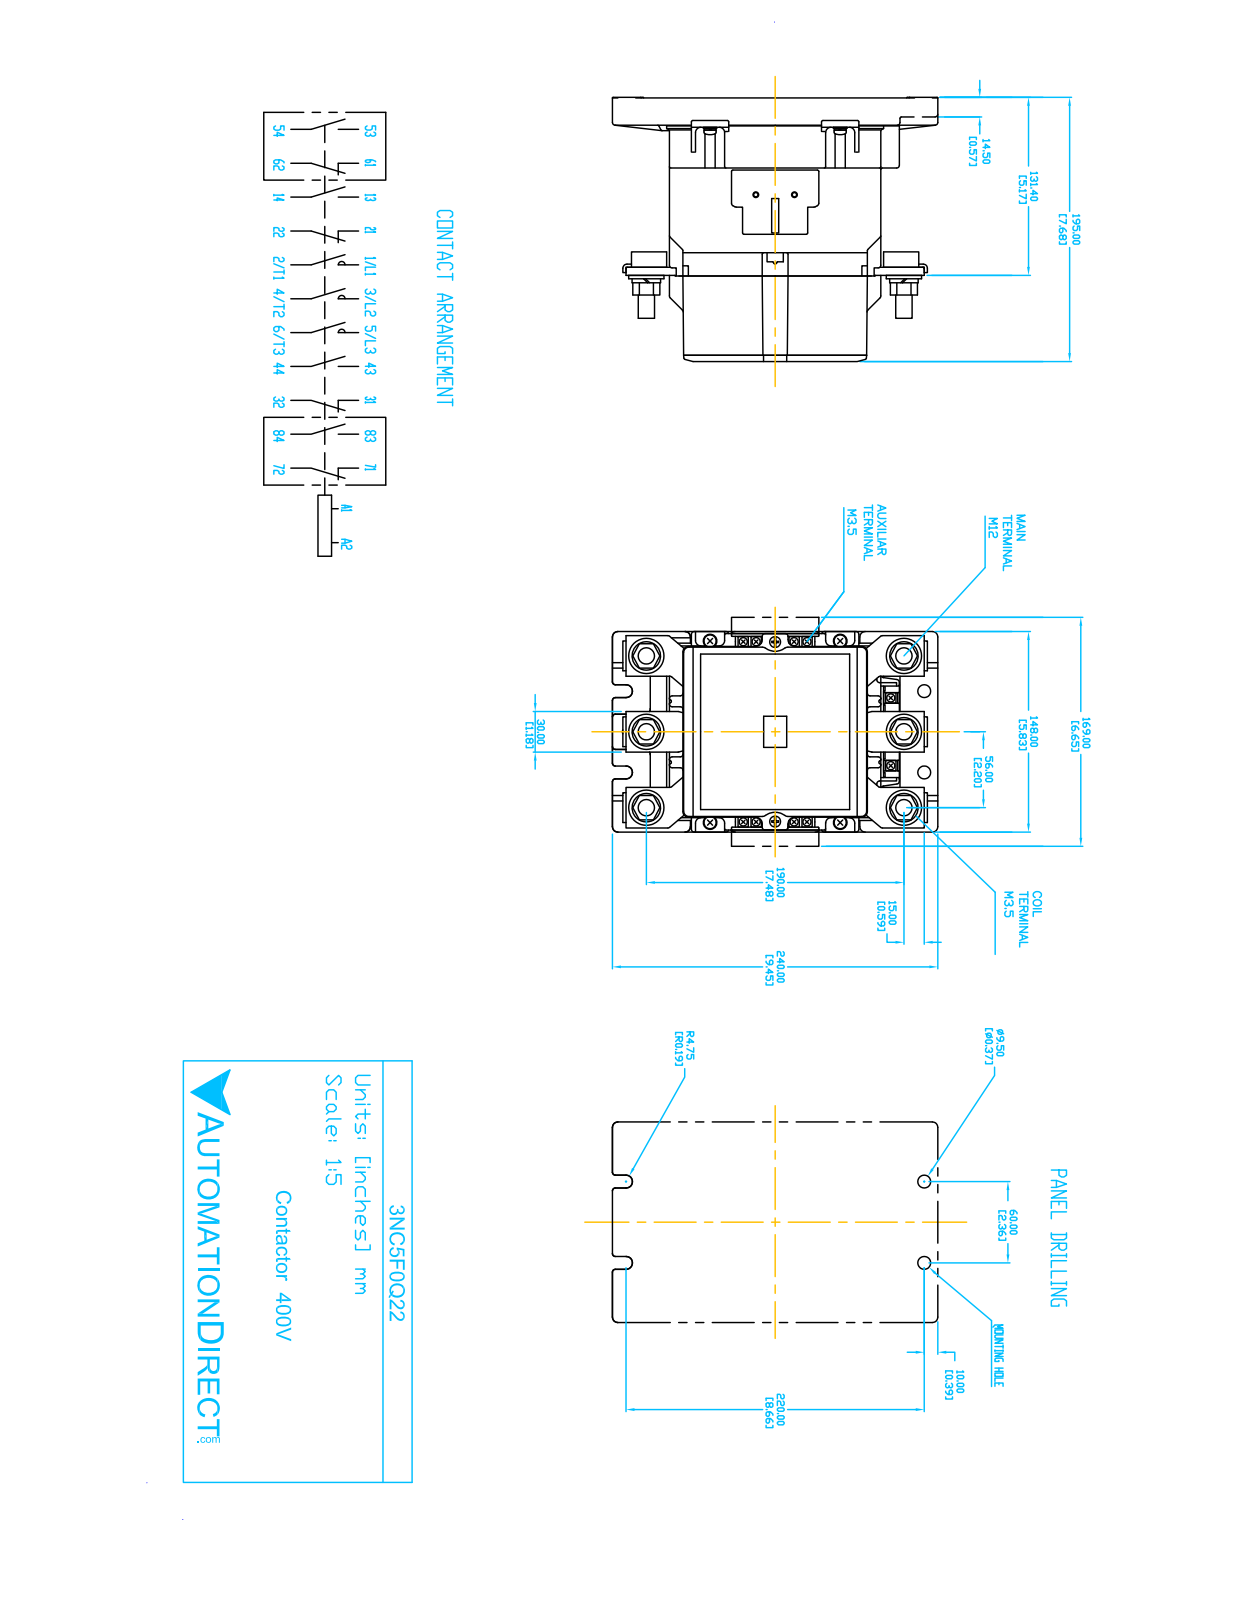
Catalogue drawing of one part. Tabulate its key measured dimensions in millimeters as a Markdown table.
| quantity | value |
| --- | --- |
| part name | 3NC5F0Q22 |
| STEP written by | SolidWorks 2018 (AUTOMOTIVE_DESIGN) |
| units | millimeters |
| bodies | 20 solids, 375 faces (261 planar, 114 cylindrical, 0 other) |
| overall size | 240 × 195 × 149 |
| volume | 4 197 000 mm³ |
| surface area | 278 100 mm² |
| round holes (diameter × count) | 12 × 6, 8 × 2, 10 × 2 |
| partial cylindrical surfaces (radius × count) | 2 × 26, 4 × 16, 1 × 12, 0.8 × 8, 5 × 6, 0.5 × 2 |
| main face-to-face distances | 115, 11, 126, 10, 146, 137, 80, 195, 21, 94 |
| hole center spacings | 57, 95.6, 116.8, 157, 198.4, 190, 30.8, 33.6 |
